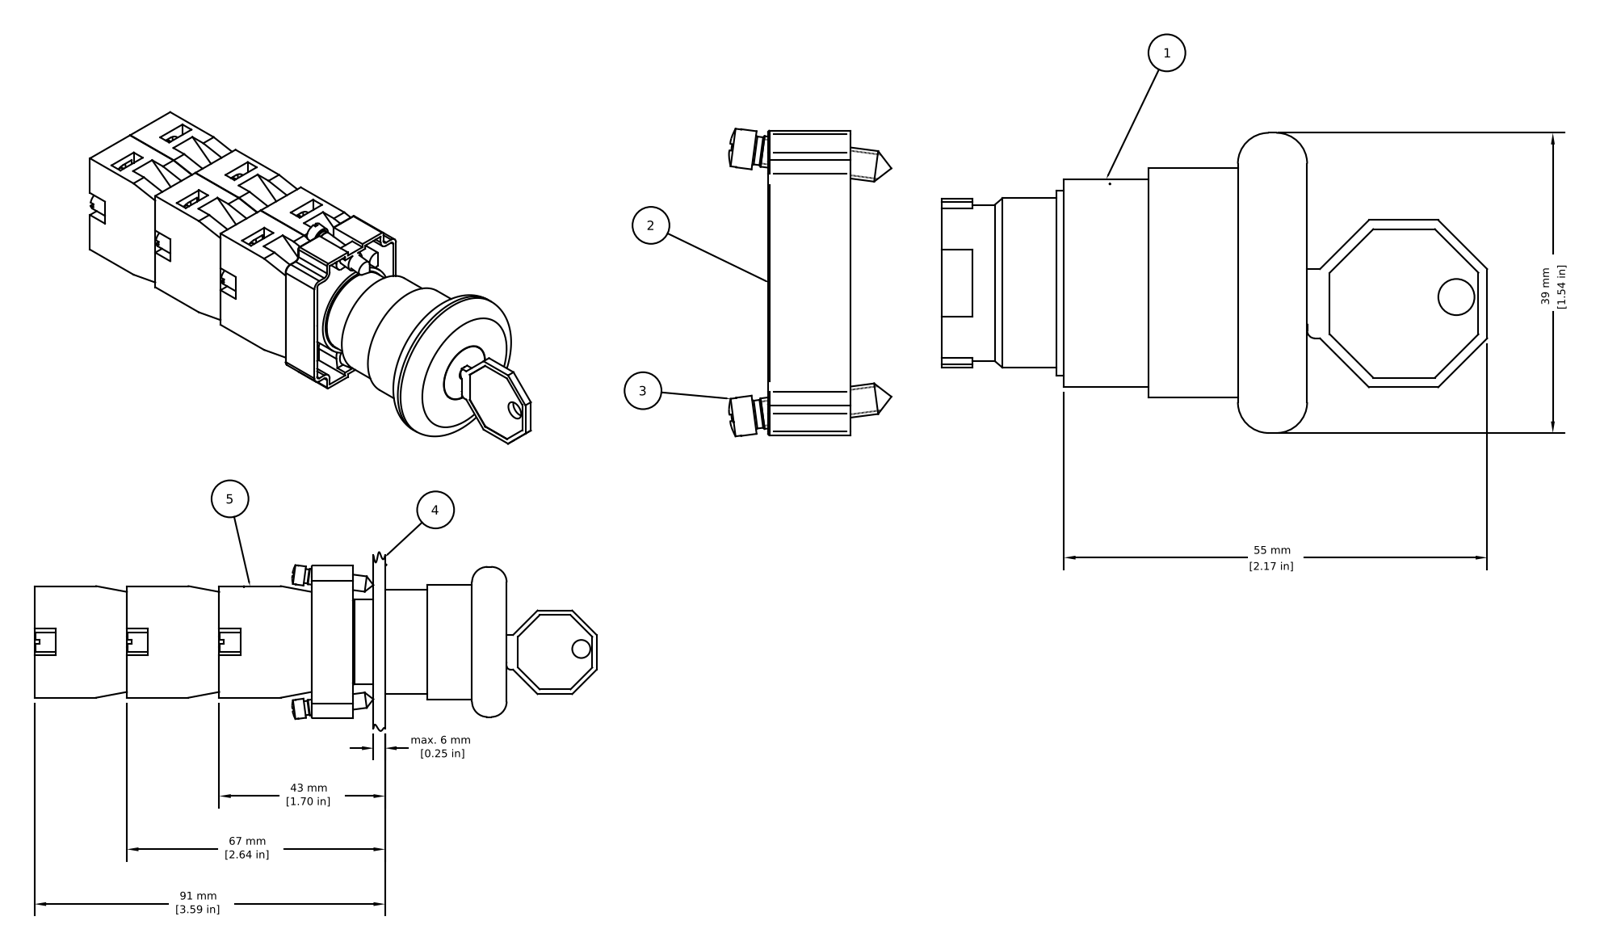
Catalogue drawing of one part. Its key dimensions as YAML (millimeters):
part_name: "2AMLKBx_assembly; 2AMLKBx; rubber_gasket; 2KY455 (+7 more)"
step_written_by: "Autodesk Inventor 2008 (AUTOMOTIVE_DESIGN)"
units: millimeters
bodies: {solids: 31, faces: 1271, planar: 706, cylindrical: 197, other: 368}
overall_size: [146.1, 60.45, 45]
volume: 91677
surface_area: 50078
round_holes:
  - {diameter: 2.5, count: 5}
  - {diameter: 2.6, count: 2}
  - {diameter: 15.2, count: 1}
  - {diameter: 18, count: 1}
  - {diameter: 22, count: 1}
  - {diameter: 22.25, count: 1}
  - {diameter: 22.5, count: 1}
  - {diameter: 25, count: 1}
  - {diameter: 27.1, count: 1}
round_bosses_or_shafts:
  - {diameter: 3, count: 6}
  - {diameter: 5, count: 4}
  - {diameter: 2.75, count: 4}
  - {diameter: 1.5, count: 4}
  - {diameter: 4, count: 2}
  - {diameter: 3.65, count: 2}
  - {diameter: 39, count: 1}
  - {diameter: 29.8, count: 1}
partial_cylinders:
  - {radius: 1, count: 15}
  - {radius: 0.25, count: 14}
  - {radius: 0.72, count: 8}
  - {radius: 2, count: 6}
  - {radius: 2.25, count: 5}
  - {radius: 0.5, count: 4}
  - {radius: 0.8, count: 4}
  - {radius: 1.8, count: 4}
face_to_face_distances: [14.8, 14.7, 24, 3, 48, 29.5, 29, 1, 19.1, 40.1]
hole_center_spacings: [14.53, 6.52, 6.57, 13, 25.88, 26, 26.27, 29.07]
